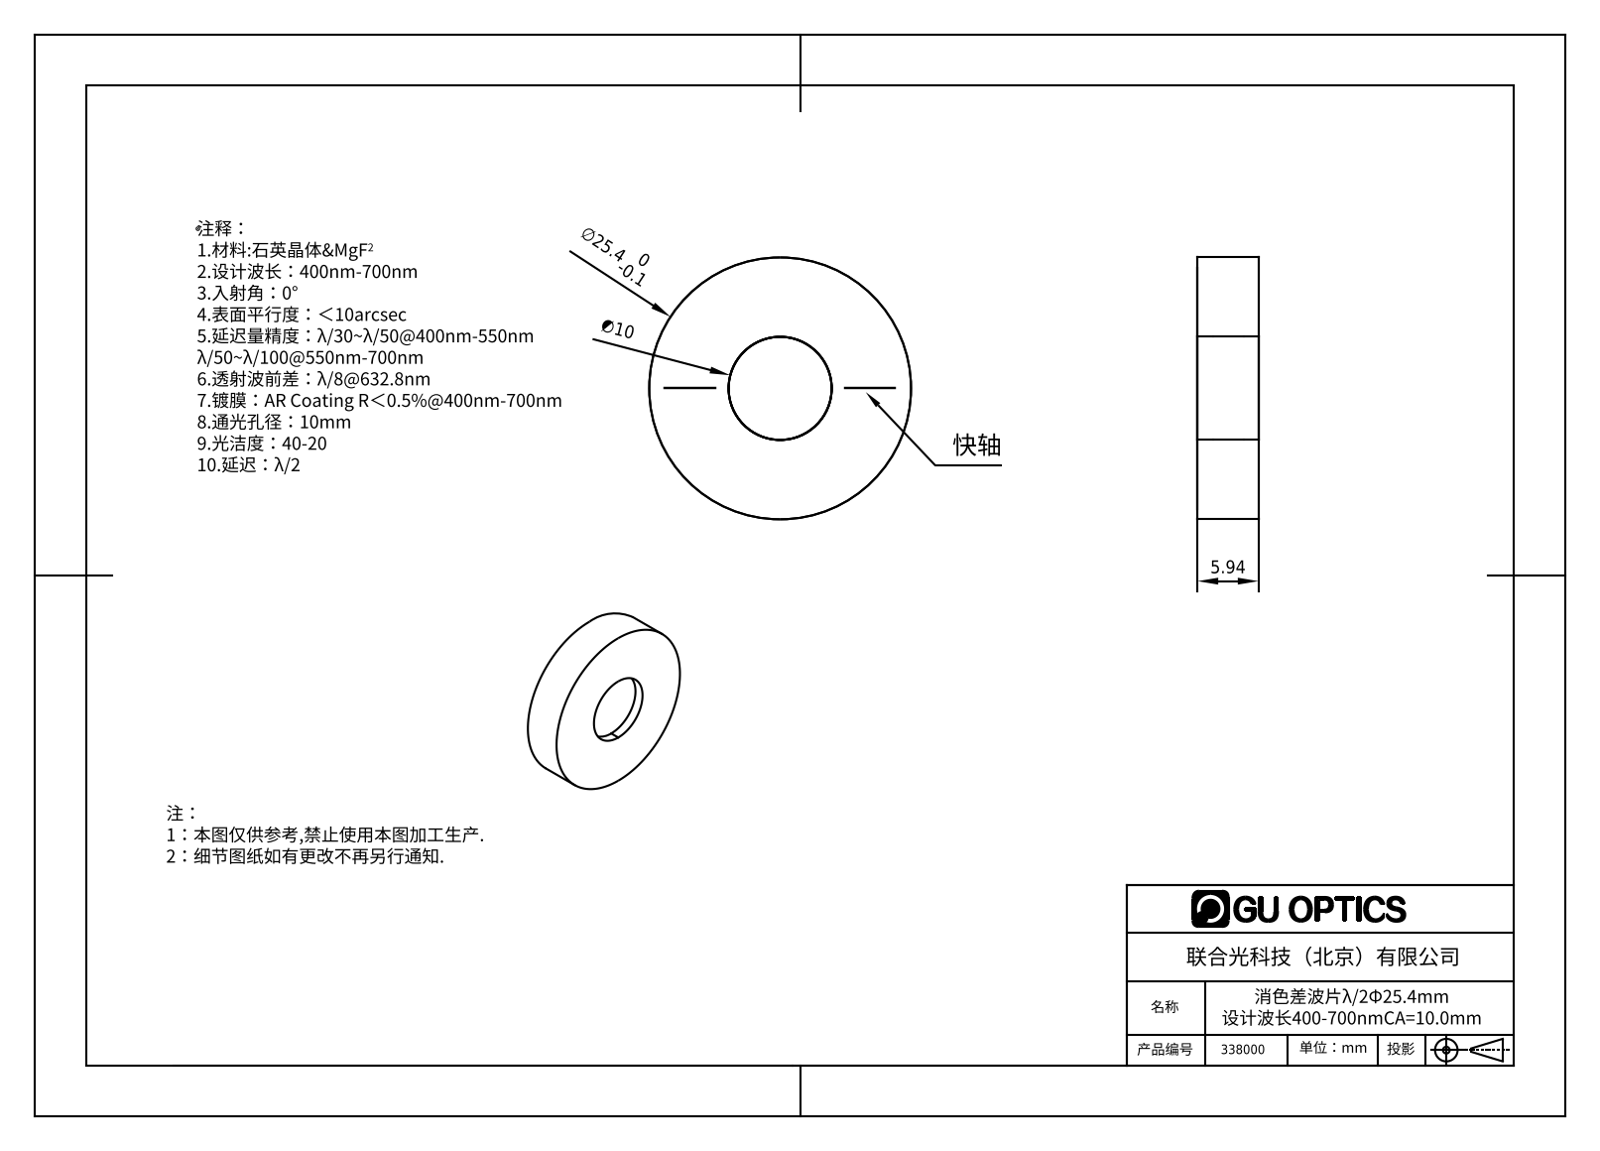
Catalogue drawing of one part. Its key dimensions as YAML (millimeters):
part_name: "338000"
step_written_by: "SolidWorks 2020 (CONFIG_CONTROL_DESIGN)"
units: millimeters
bodies: {solids: 4, faces: 24, planar: 10, cylindrical: 14, other: 0}
overall_size: [25.4, 25.4, 5.9]
volume: 3279
surface_area: 3346
round_holes:
  - {diameter: 10, count: 1}
  - {diameter: 23.4, count: 1}
round_bosses_or_shafts:
  - {diameter: 25.4, count: 1}
  - {diameter: 15, count: 1}
face_to_face_distances: [2.95, 1.5, 1.45, 4.4, 5.9, 4.45]
